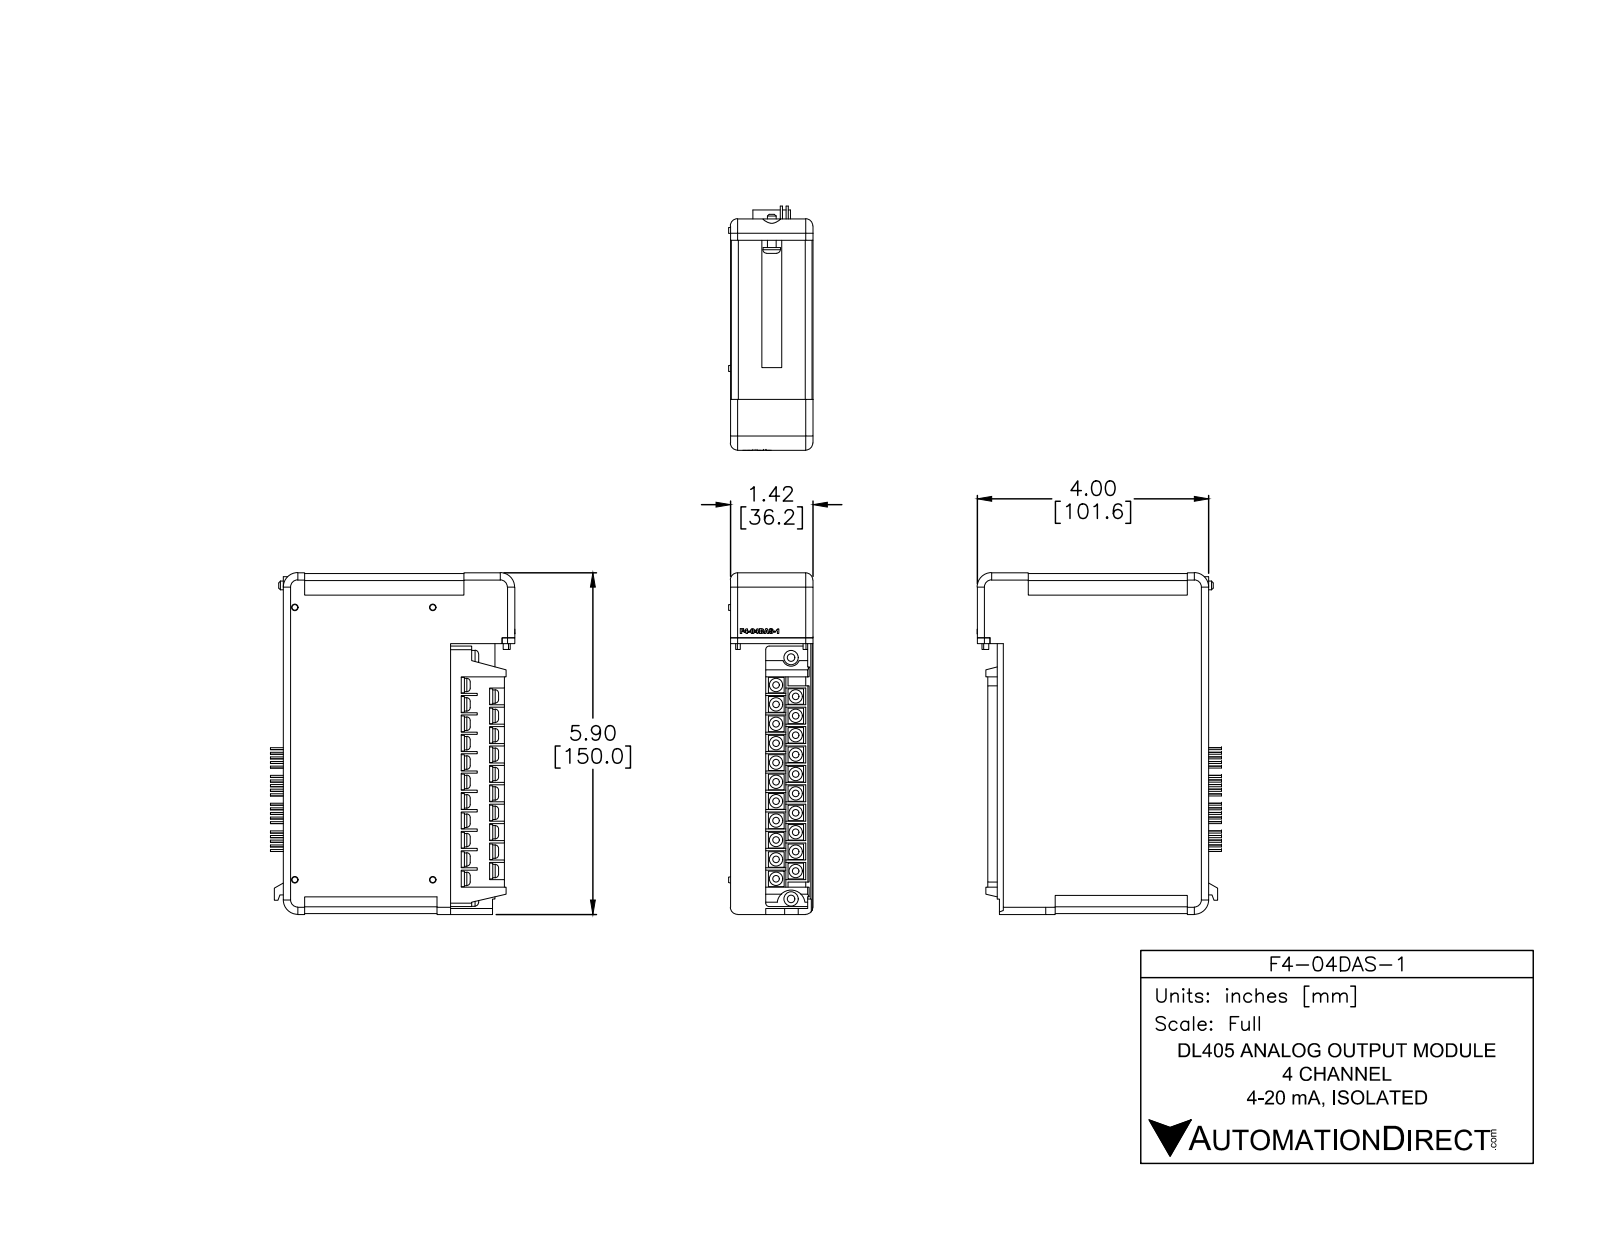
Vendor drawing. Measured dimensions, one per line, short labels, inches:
name: F4-04DAS-1
written by: SolidWorks 2014 (AUTOMOTIVE_DESIGN)
unit: in
bodies: 6 solids, 914 faces (572 planar, 246 cylindrical, 96 other)
size: 5.905 × 4.223 × 1.455
volume: 27.6 in³; area: 90.48 in²
bosses: 21× ⌀0.23, 20× ⌀0.035, 20× ⌀0.035, 2× ⌀0.25, 1× ⌀0.3, 1× ⌀0.15
rounds: 82× R0.015, 8× R0.125, 4× R0.12, 3× R0.25, 2× R0.03, 2× R0.06, 1× R0.149, 1× R0.151
face distances: 1.425, 0.015, 2.89, 5.875, 1.41, 0.47, 0.955, 5.89, 1.21, 0.345
